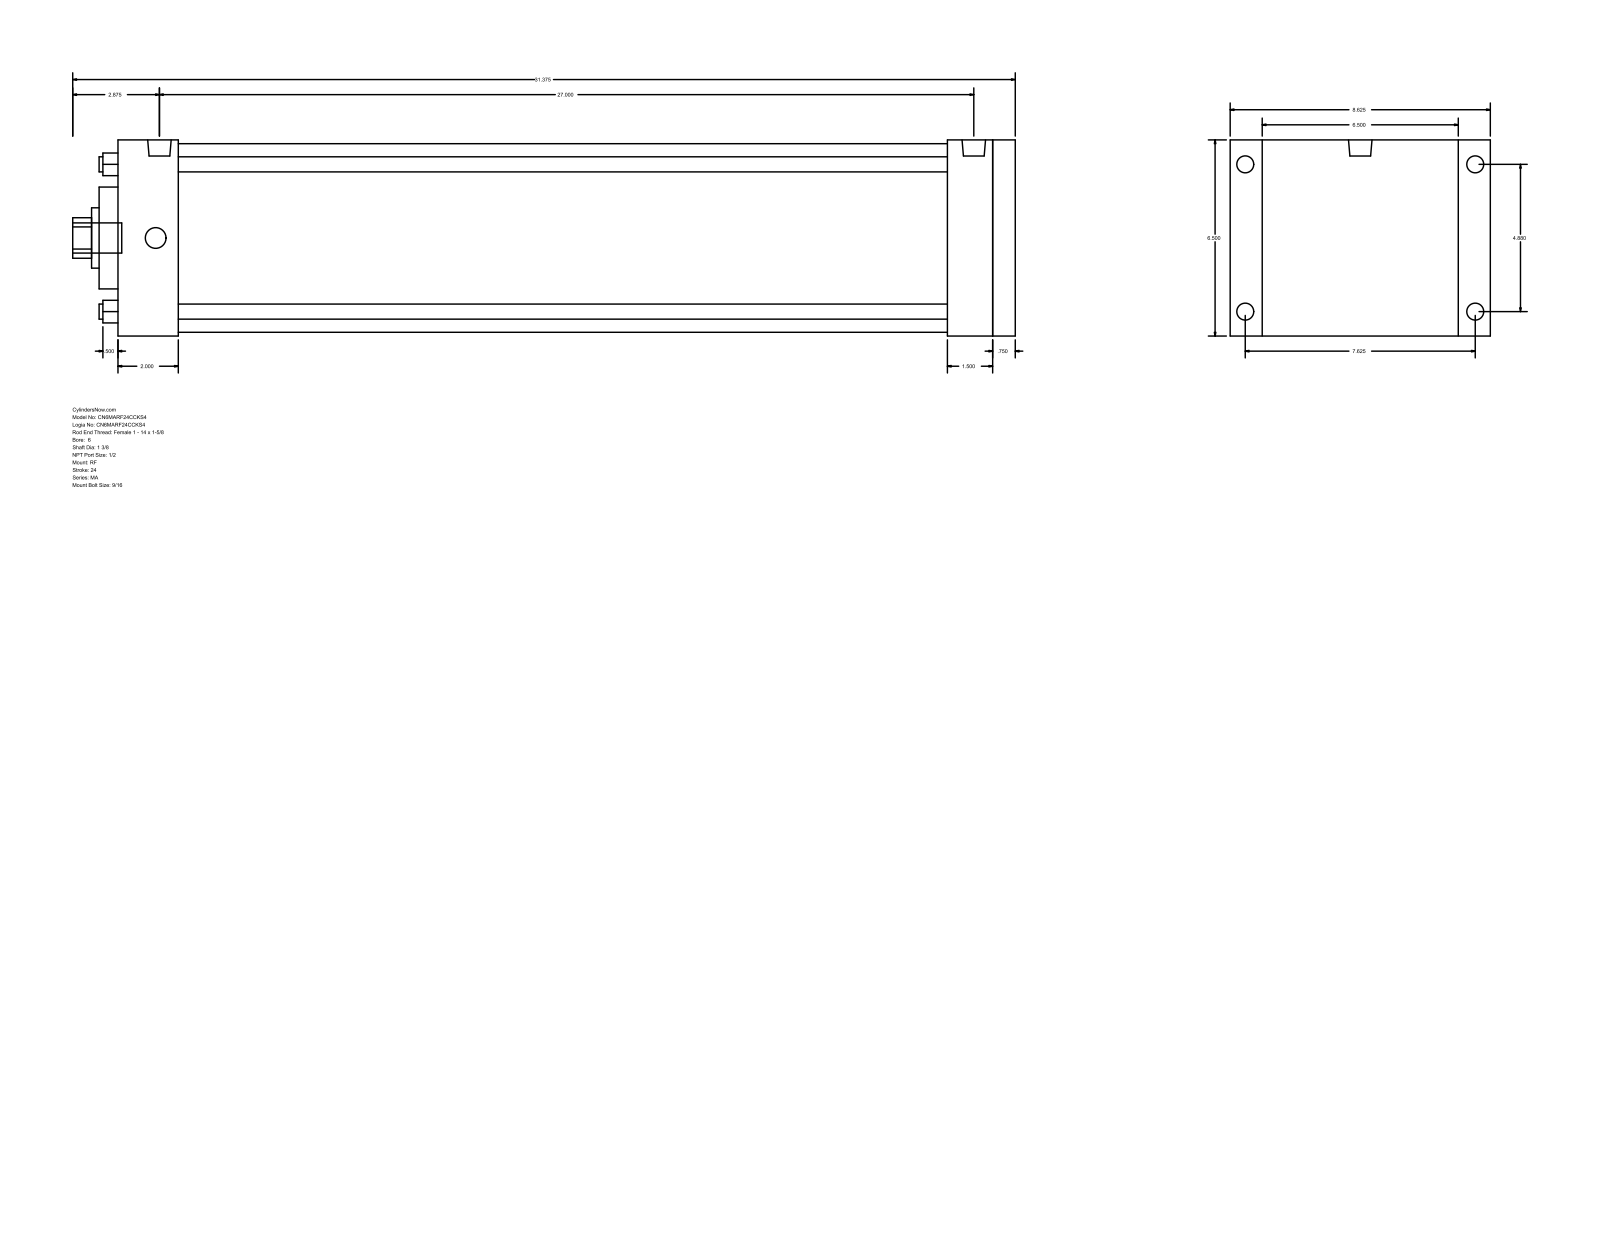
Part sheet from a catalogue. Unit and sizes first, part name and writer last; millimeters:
Units: millimetres
Overall size (bounding box): 796.92 × 219.07 × 165.1
Round holes (diameter × count): ⌀12.7 ×4, ⌀34.92 ×1, ⌀50.8 ×1, ⌀85.72 ×1, ⌀158.75 ×1
Round bosses / shafts (diameter × count): ⌀17.46 ×4, ⌀14.29 ×4, ⌀19.77 ×2, ⌀25.4 ×1
Partial cylindrical surfaces — rounded edges, fillets, slot ends (radius × count): R17.06 ×1
Main face-to-face distances: 165.1, 758.82, 19.04, 739.78, 50.8, 688.98, 708.02, 701.67, 650.87, 38.11
Hole centre spacings: 87.65, 123.96, 175.31
Bodies: 0 solids, 94 faces (65 planar, 29 cylindrical, 0 other)
Part name (STEP PRODUCT): MA_RF__0600_1.375
STEP written by: GSSL Pune (CONFIG_CONTROL_DESIGN)
